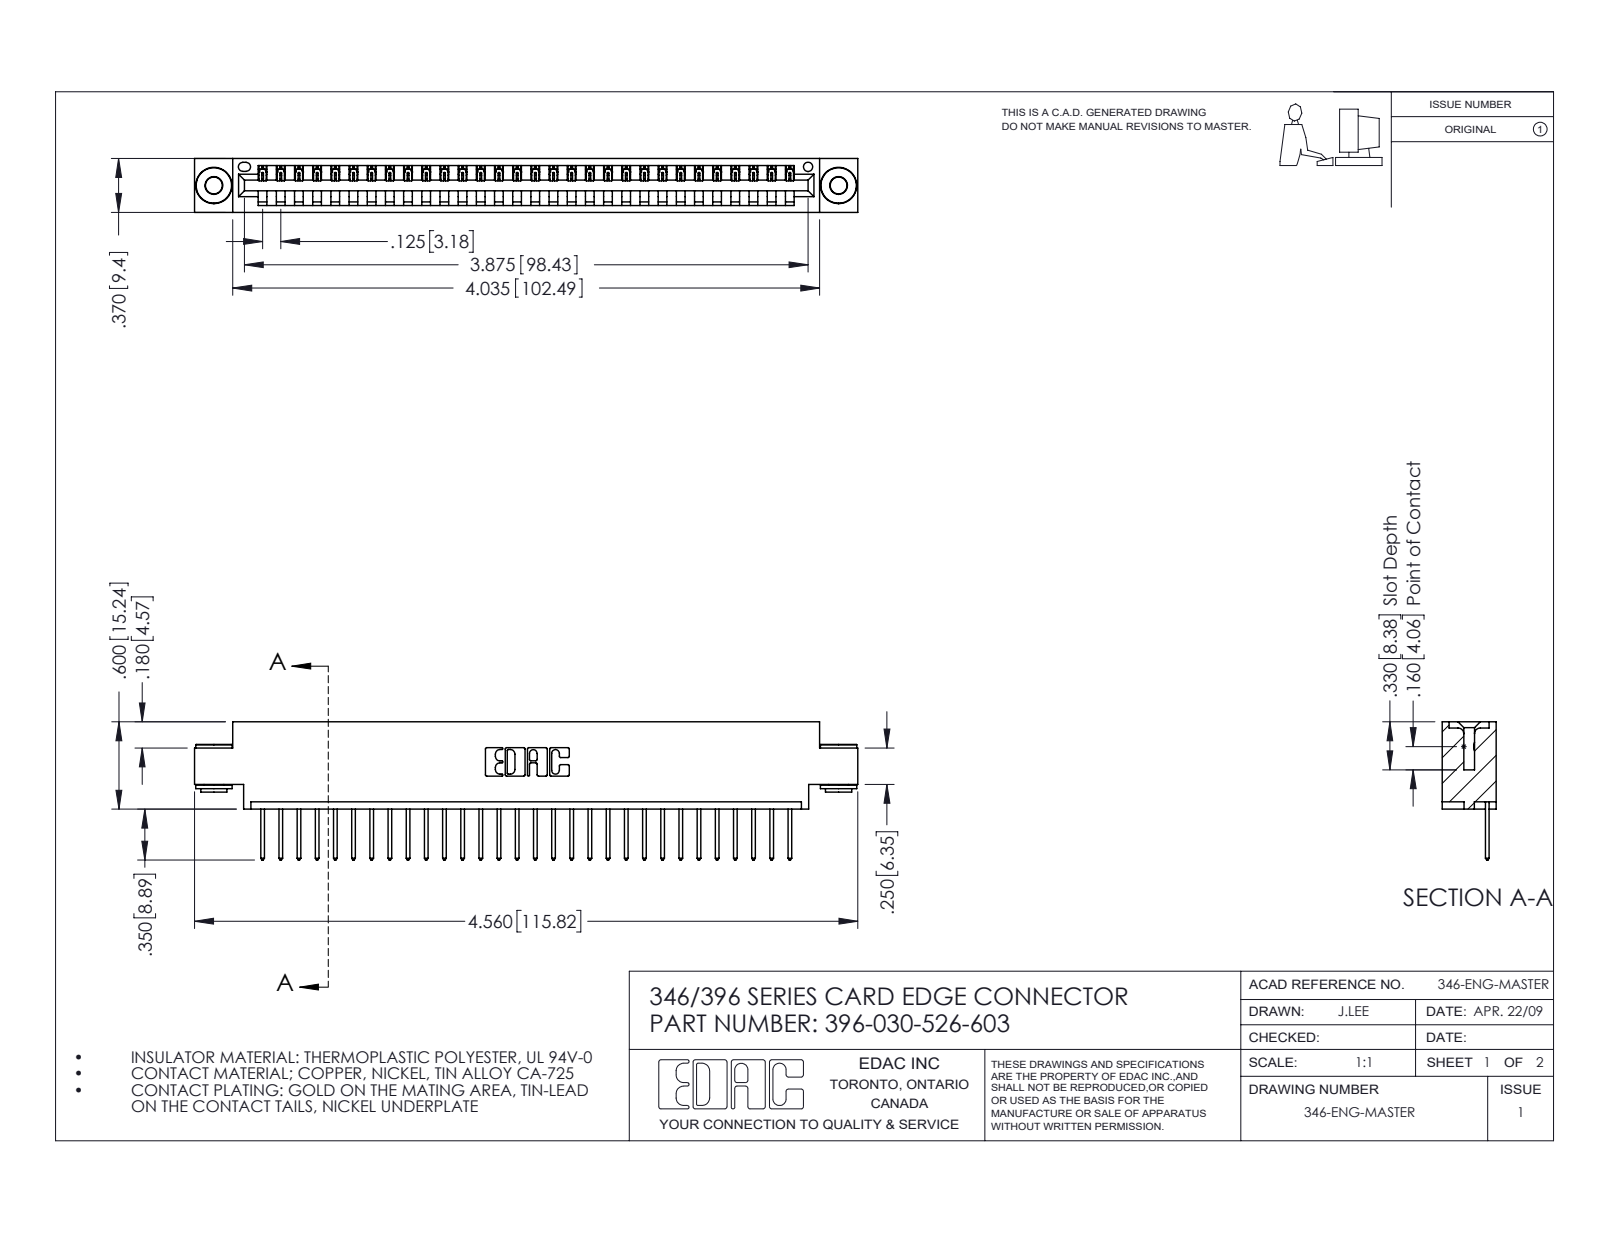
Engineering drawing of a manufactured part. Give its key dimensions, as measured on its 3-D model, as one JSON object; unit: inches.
{"part_name": "396-030-526-603; 345-292-001_345-293-126; 346 Part_0.170 Offset - 0.156 Dia-TH; 345-250-002_345-250-002-102", "step_written_by": "SolidWorks 2016 (CONFIG_CONTROL_DESIGN)", "units": "inches", "bodies": {"solids": 33, "faces": 1904, "planar": 1290, "cylindrical": 606, "other": 8}, "overall_size": [4.56, 0.95, 0.37], "volume_in3": 0.662, "surface_area_in2": 21.35, "round_holes": [[0.116, 2], [0.156, 2], [0.064, 1]], "round_bosses_or_shafts": [[0.25, 2], [0.18, 2], [0.136, 2]], "partial_cylinders_radius": [[0.006, 60], [0.01, 60], [0.01, 22], [0.007, 6], [0.031, 6], [0.026, 3], [0.031, 2], [0.04, 2]], "face_to_face_distances": [0.048, 0.322, 0.37, 0.25, 0.025, 0.072, 0.298, 0.148, 0.222, 0.1], "hole_center_spacings": [0.246, 4.087, 4.295]}
